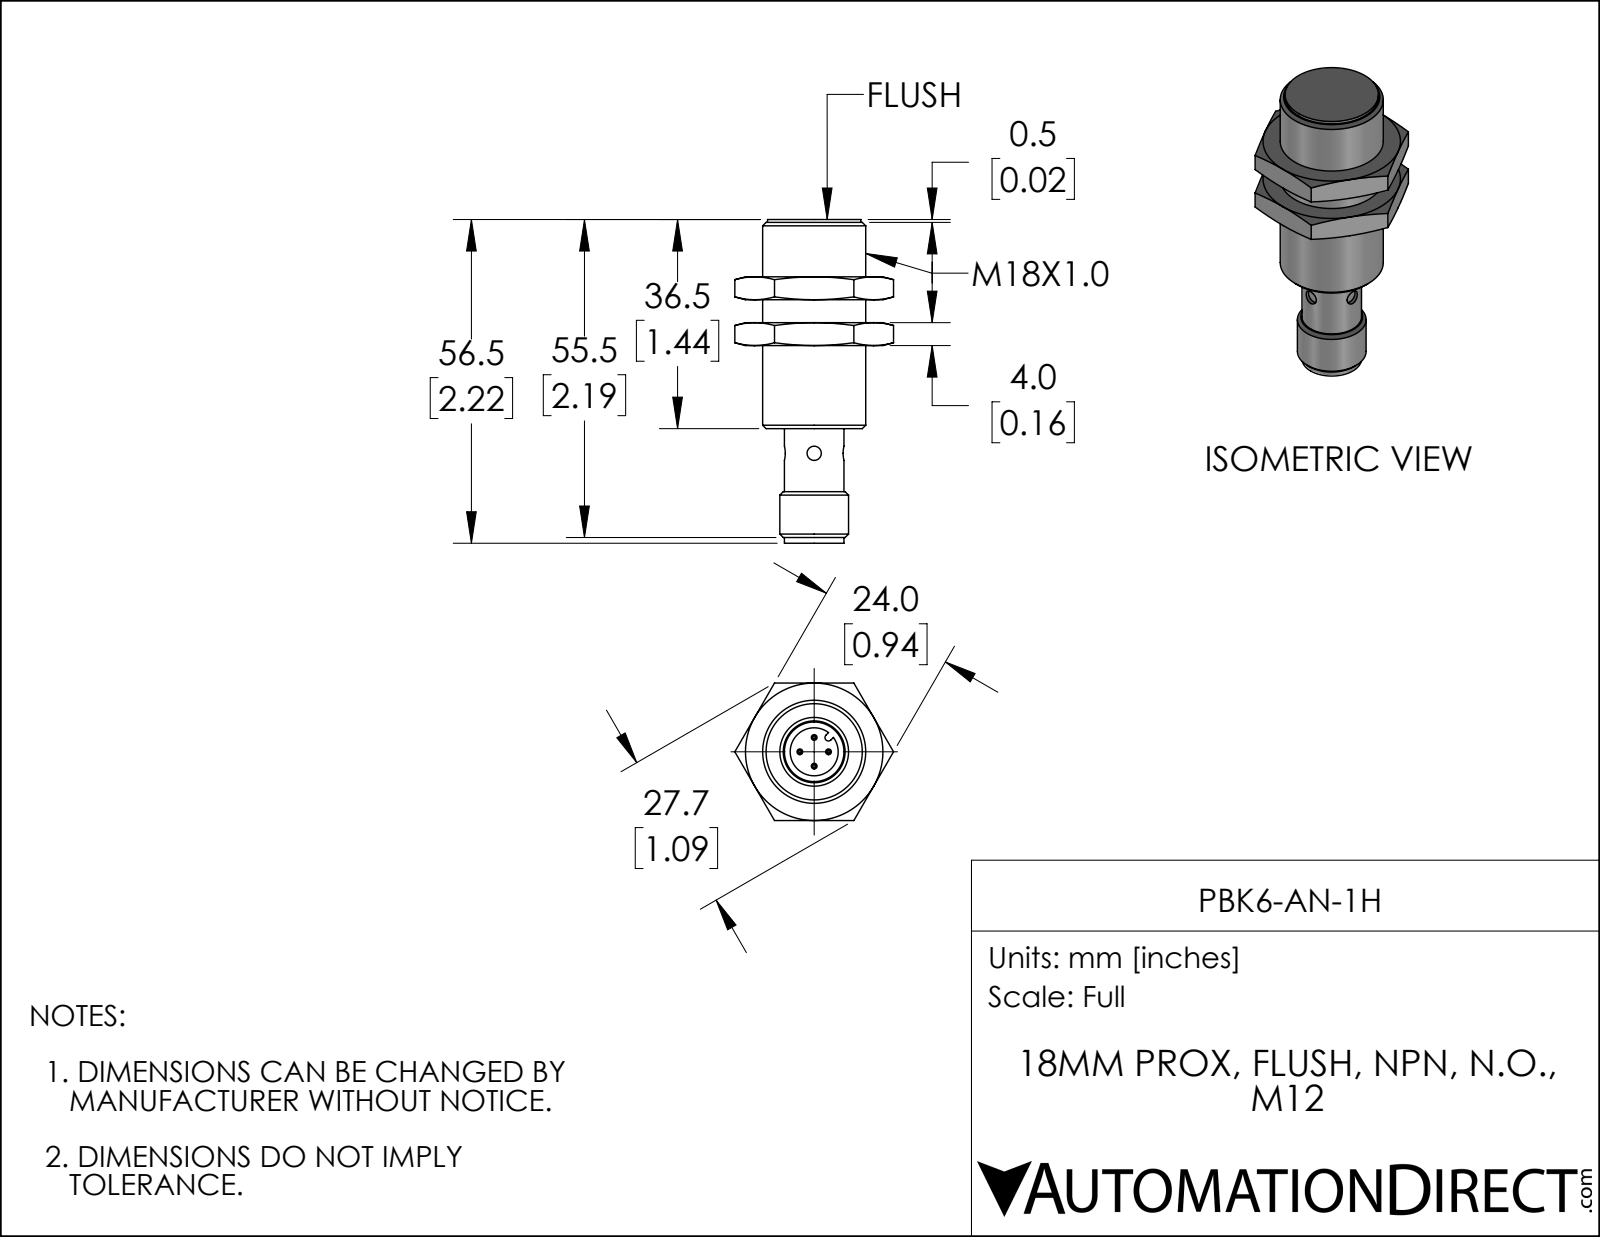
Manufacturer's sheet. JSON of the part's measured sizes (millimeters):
{"part_name": "DSD-0326", "step_written_by": "SolidWorks 2019 (AUTOMOTIVE_DESIGN)", "units": "millimeters", "bodies": {"solids": 1, "faces": 40, "planar": 17, "cylindrical": 15, "other": 8}, "overall_size": [56.5, 18, 18], "volume_mm3": 10700, "surface_area_mm2": 3616, "round_holes": [[2.5, 2], [8.4, 1]], "round_bosses_or_shafts": [[1, 4], [18, 1], [16.3, 1], [12, 1], [10.4, 1]], "partial_cylinders_radius": [[0.6, 1]], "face_to_face_distances": [36.5, 47.6, 11.1, 56.5, 20, 8.9, 9, 0.5, 36, 47.1]}
